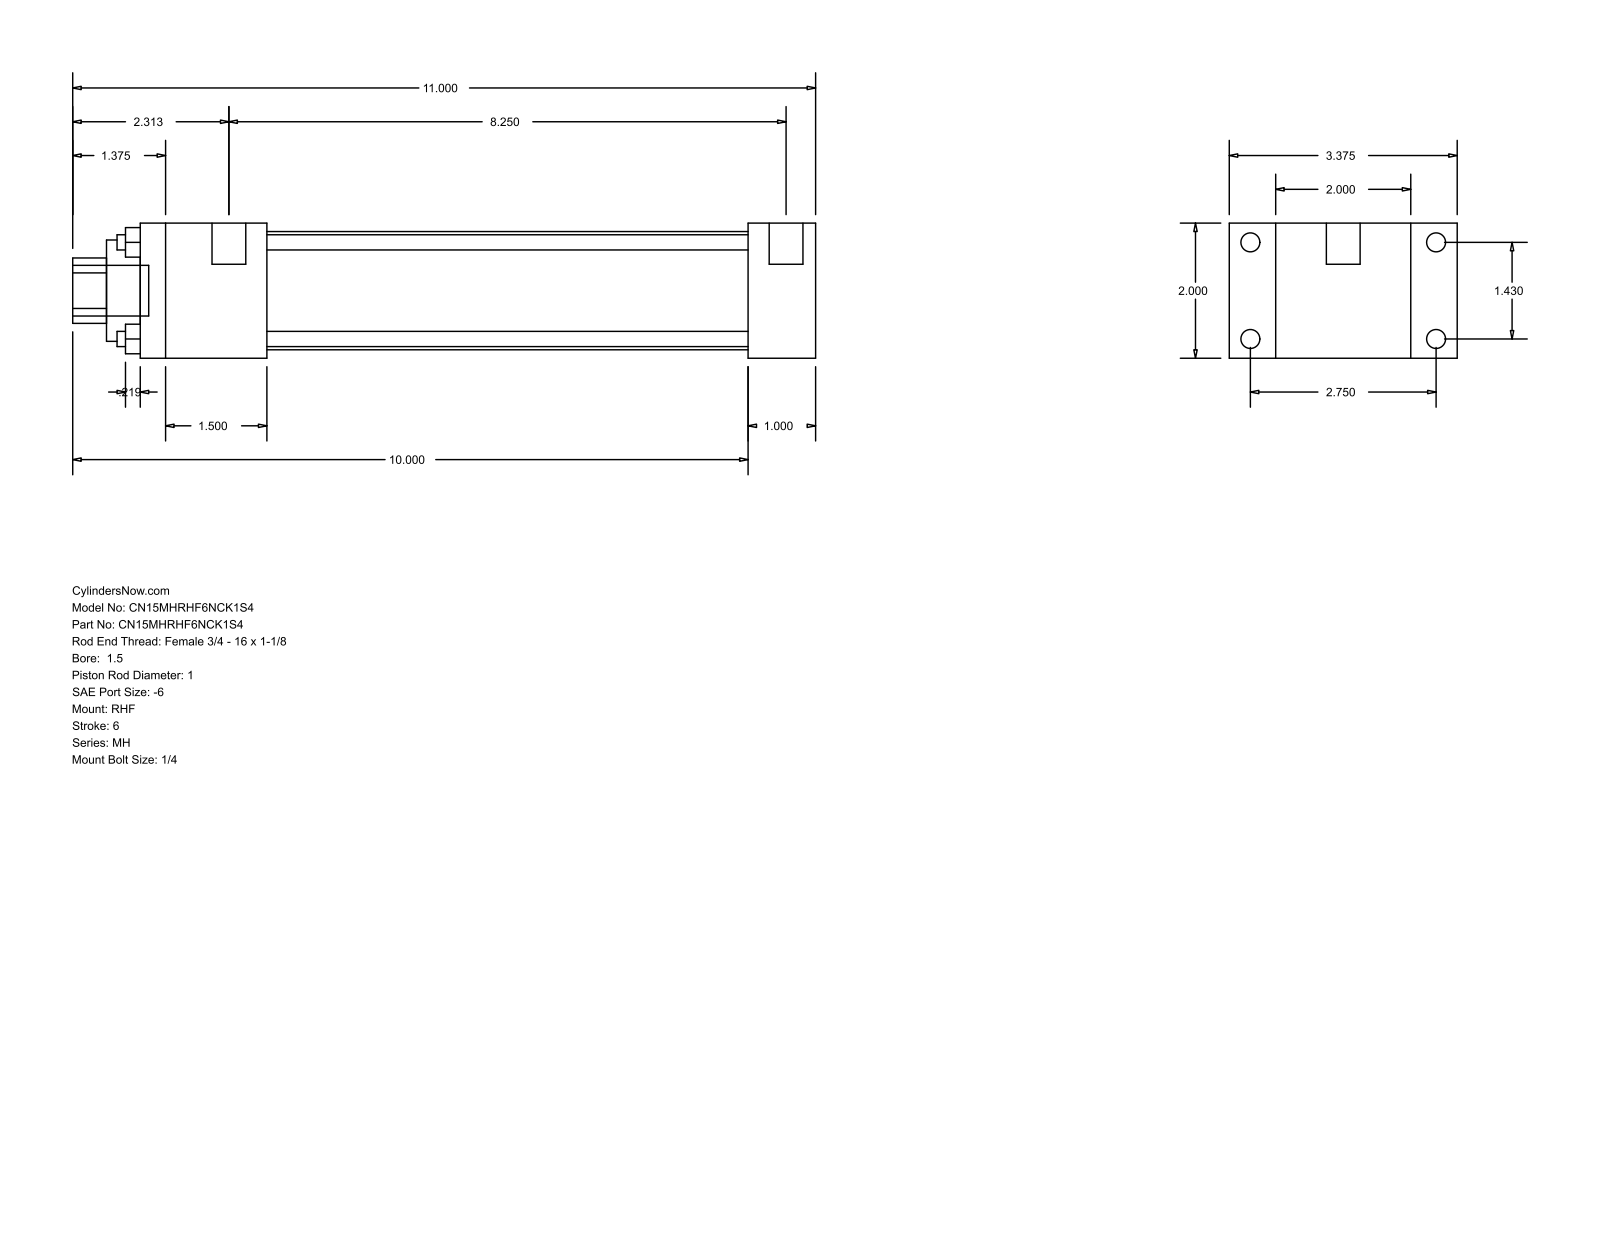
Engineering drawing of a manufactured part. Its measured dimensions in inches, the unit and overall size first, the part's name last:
Units: inches
Overall size (bounding box): 11 × 3.375 × 2
Round holes (diameter × count): ⌀0.225 ×4, ⌀1 ×1, ⌀1.5 ×1, ⌀1.75 ×1
Round bosses / shafts (diameter × count): ⌀0.281 ×4, ⌀0.219 ×4, ⌀0.5 ×2, ⌀0.75 ×1
Partial cylindrical surfaces — rounded edges, fillets, slot ends (radius × count): R0.484 ×1
Main face-to-face distances: 2, 1, 0.687, 2.687, 3.375, 10, 9, 1.875, 7.125, 8.125
Hole centre spacings: 1.011, 1.43, 2.022
Bodies: 0 solids, 88 faces (60 planar, 28 cylindrical, 0 other)
Part name (STEP PRODUCT): MH_RHF__0150_1
STEP written by: GSSL Pune (CONFIG_CONTROL_DESIGN)
